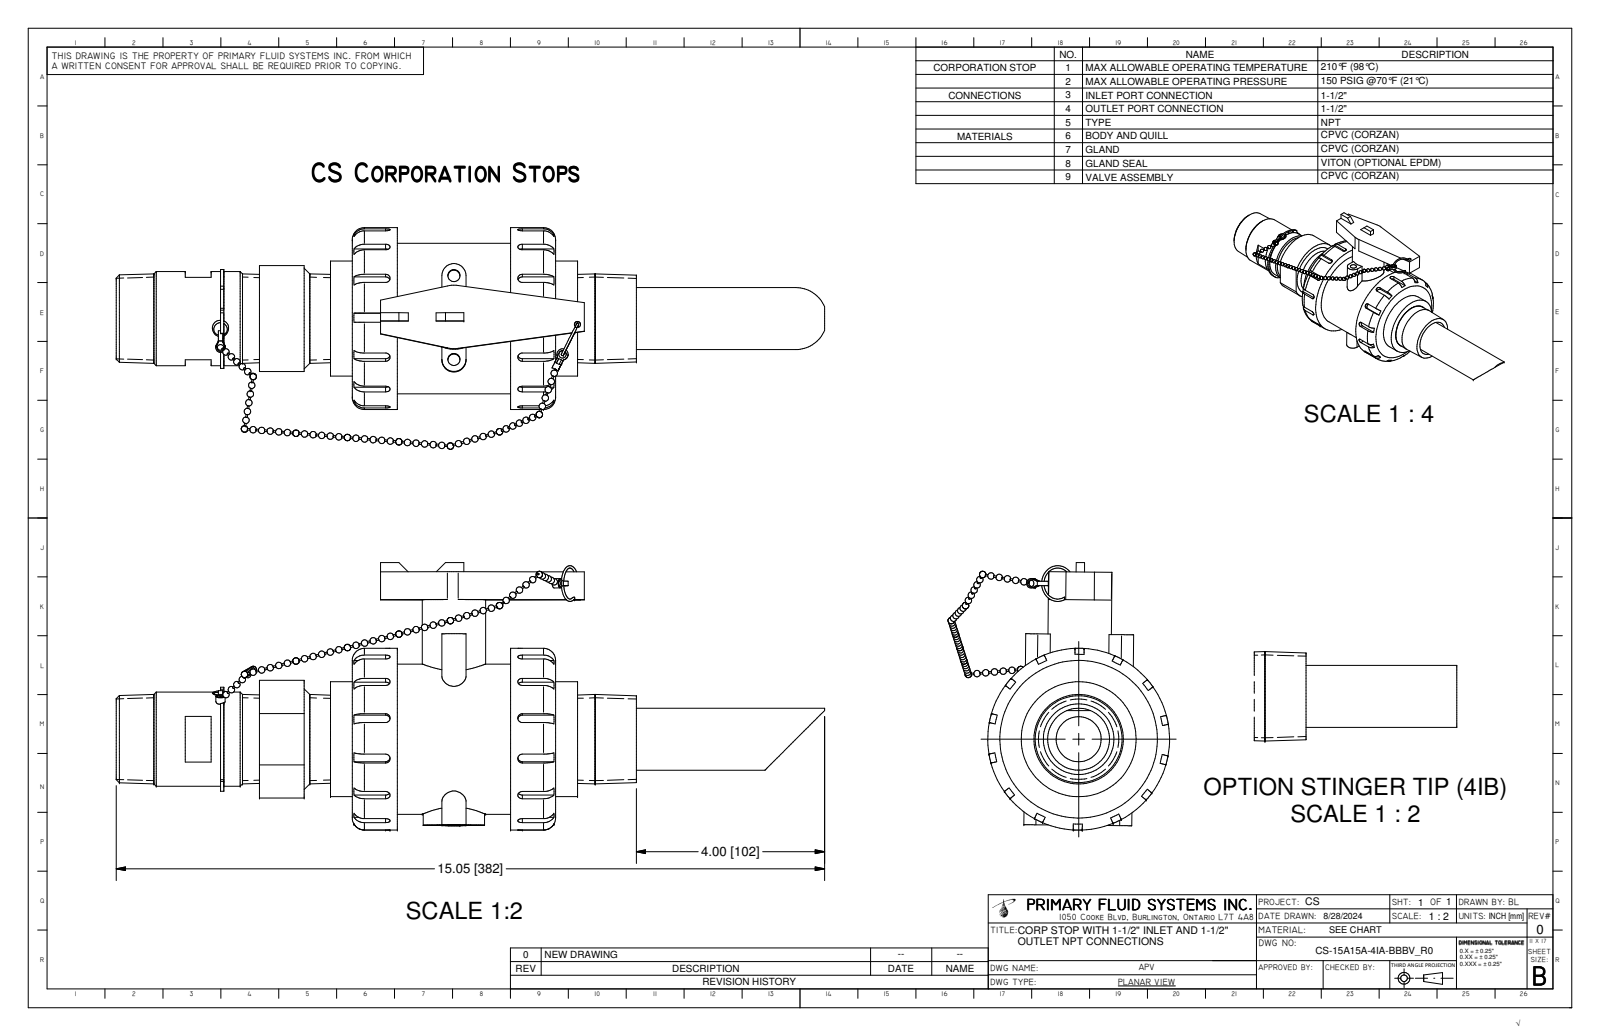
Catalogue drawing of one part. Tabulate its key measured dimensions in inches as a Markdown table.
| quantity | value |
| --- | --- |
| STEP written by | Autodesk Inventor 2025 (CONFIG_CONTROL_DESIGN) |
| units | inches |
| bodies | 19 solids, 428 faces (211 planar, 137 cylindrical, 80 other) |
| overall size | 15.052 × 5.683 × 4.707 |
| volume | 64.71 in³ |
| surface area | 296.8 in² |
| round holes (diameter × count) | 0.256 × 4, 0.098 × 2, 0.15 × 2, 0.157 × 2, 0.13 × 1, 0.957 × 1, 1.01 × 1, 1.049 × 1, 1.367 × 1, 1.5 × 1, 1.803 × 1, 1.9 × 1 |
| round bosses / shafts (diameter × count) | 0.035 × 9, 0.236 × 2, 3.862 × 1, 3.193 × 1, 2.441 × 1, 2 × 1, 1.8 × 1, 1.347 × 1 |
| partial cylindrical surfaces (radius × count) | 0.097 × 26, 0.049 × 2, 0.098 × 2, 0.197 × 2, 0.256 × 2, 1.049 × 1, 1.104 × 1, 1.25 × 1 |
| main face-to-face distances | 0.956, 3.365, 0.465, 1.421, 3.829, 4.785, 4.321, 2.408, 0.591, 0.102 |
| hole center spacings | 0.89, 0.891, 1.781, 2.309, 2.724, 2.828, 2.857, 0.314 |
